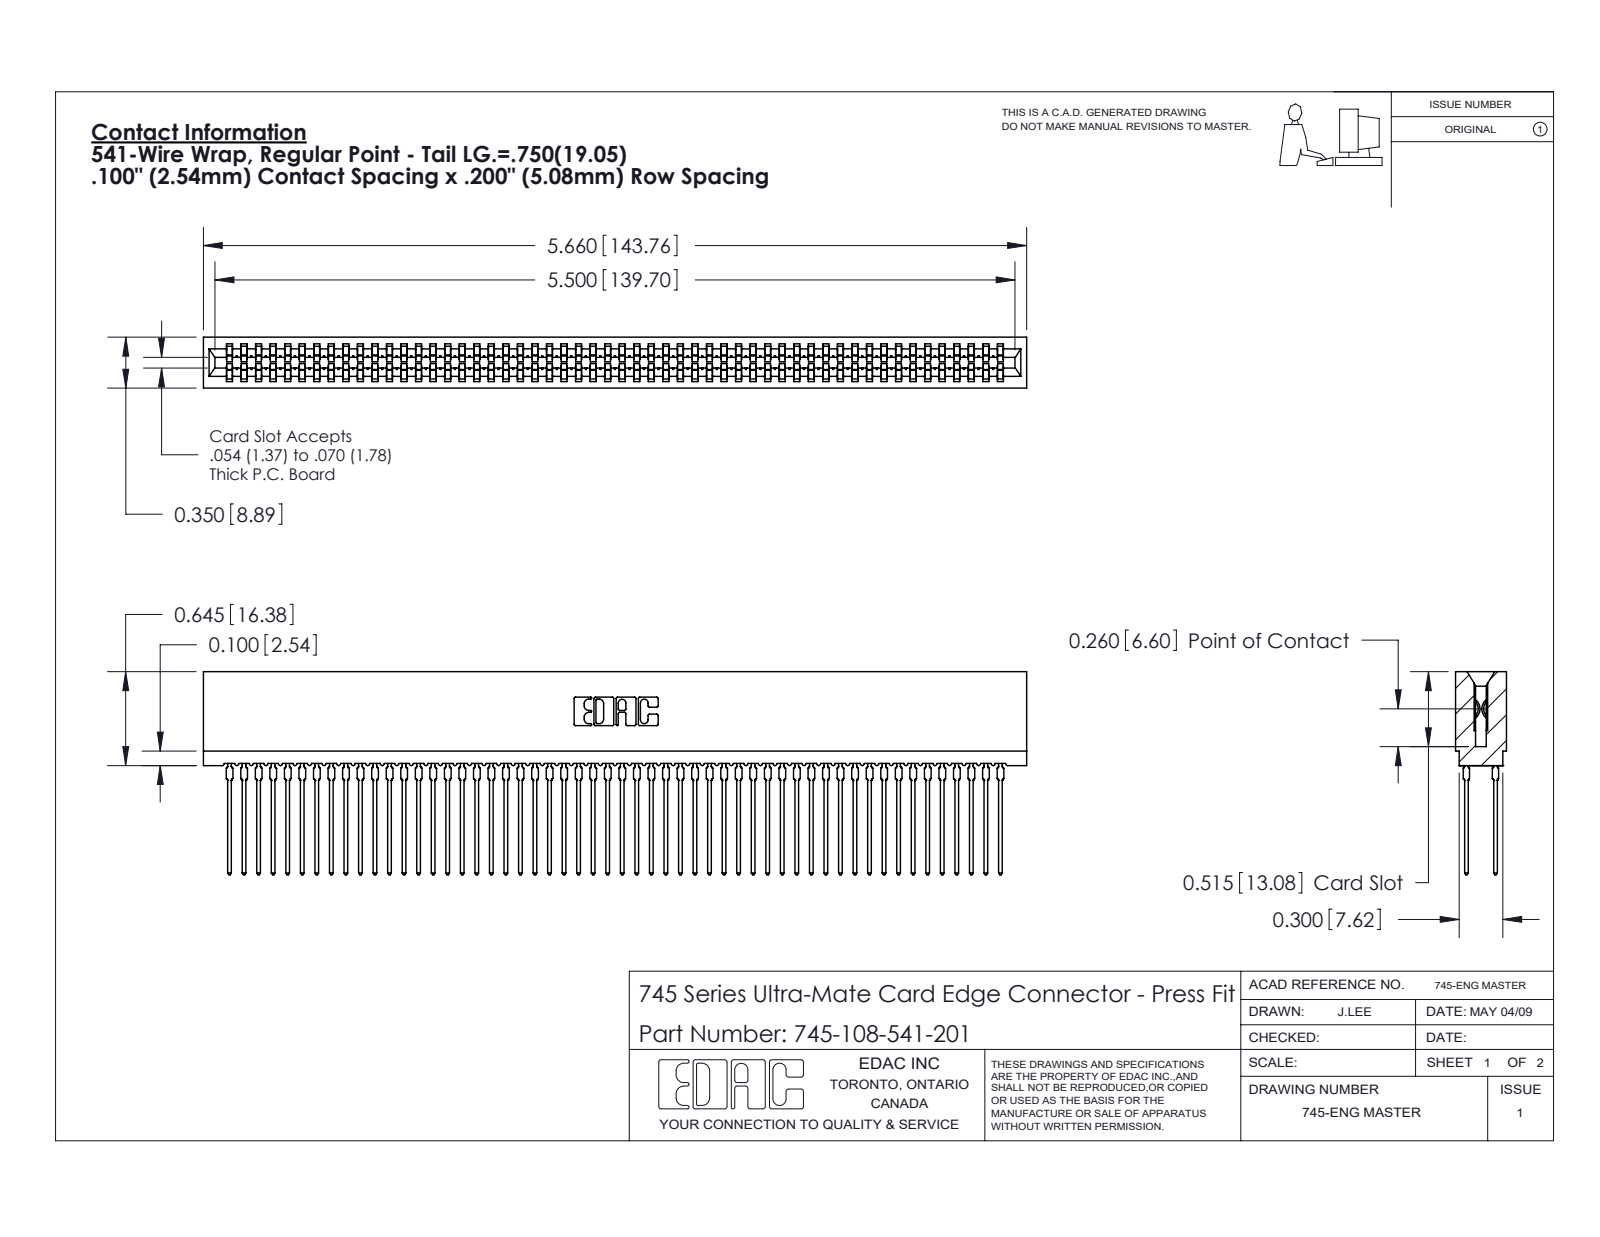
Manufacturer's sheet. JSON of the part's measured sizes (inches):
{"part_name": "745 Part_Insulator Option - 01; 745-292-001_541; 745-108-541-201", "step_written_by": "SolidWorks 2020 (CONFIG_CONTROL_DESIGN)", "units": "inches", "bodies": {"solids": 109, "faces": 9761, "planar": 5023, "cylindrical": 1930, "other": 2808}, "overall_size": [5.66, 1.396, 0.35], "volume_in3": 0.818, "surface_area_in2": 45.99, "partial_cylinders_radius": [[0.021, 216], [0.015, 108], [0.01, 22], [0.005, 8], [0.011, 8], [0.007, 6], [0.031, 6], [0.026, 3]], "face_to_face_distances": [0.063, 0.287, 0.2, 0.35, 0.087, 0.263, 0.025, 0.045, 0.305, 0.018]}
